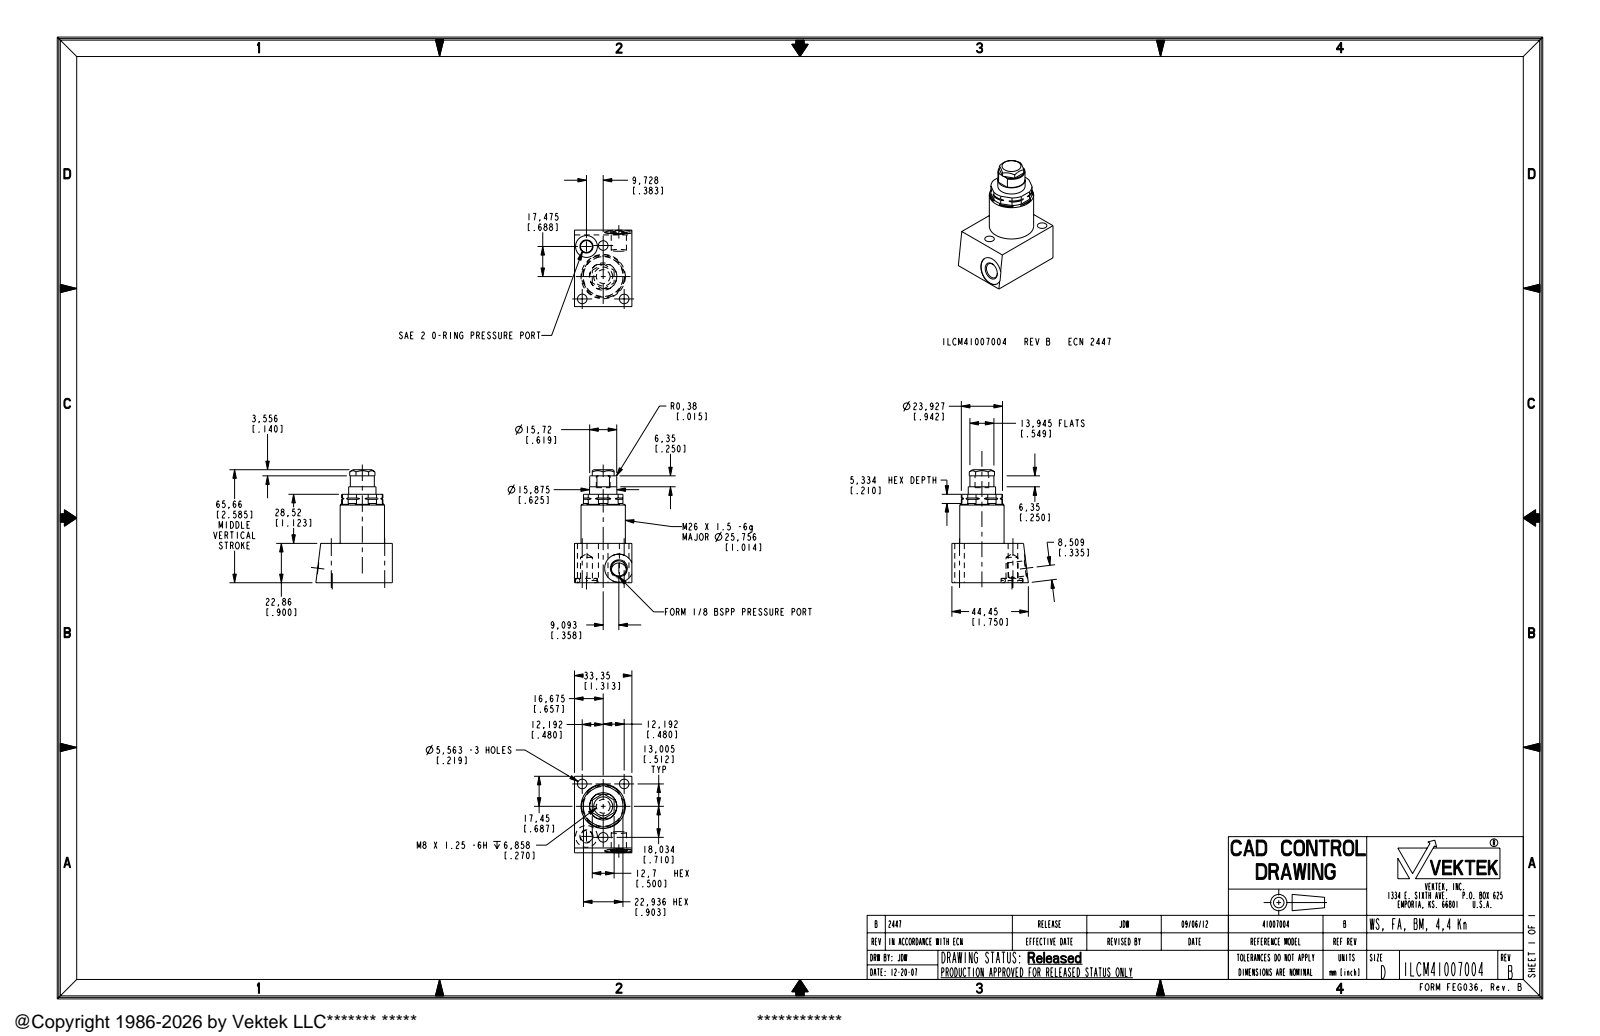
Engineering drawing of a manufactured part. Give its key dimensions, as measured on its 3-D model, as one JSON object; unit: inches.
{"part_name": "ILCM41007004", "step_written_by": "PRO/ENGINEER BY PARAMETRIC TECHNOLOGY CORPORATION, 2007460 (AUTOMOTIVE_DESIGN_CC2)", "units": "inches", "bodies": {"solids": 1, "faces": 101, "planar": 39, "cylindrical": 40, "other": 22}, "overall_size": [2.585, 1.75, 1.313], "volume_in3": 2.827, "surface_area_in2": 17.85, "round_holes": [[0.219, 3], [0.272, 1], [0.315, 1], [0.348, 1], [0.5, 1], [0.65, 1]], "round_bosses_or_shafts": [[1.014, 1], [0.625, 1]], "partial_cylinders_radius": [[0.02, 6], [0.309, 1], [0.471, 1]], "face_to_face_distances": [1.313, 0.9, 2.023, 1.123, 0.202, 0.702, 0.903, 2.585, 1.685, 0.562], "hole_center_spacings": [0.384, 0.702, 0.702, 0.71, 0.788, 0.96, 1.204, 1.313]}
